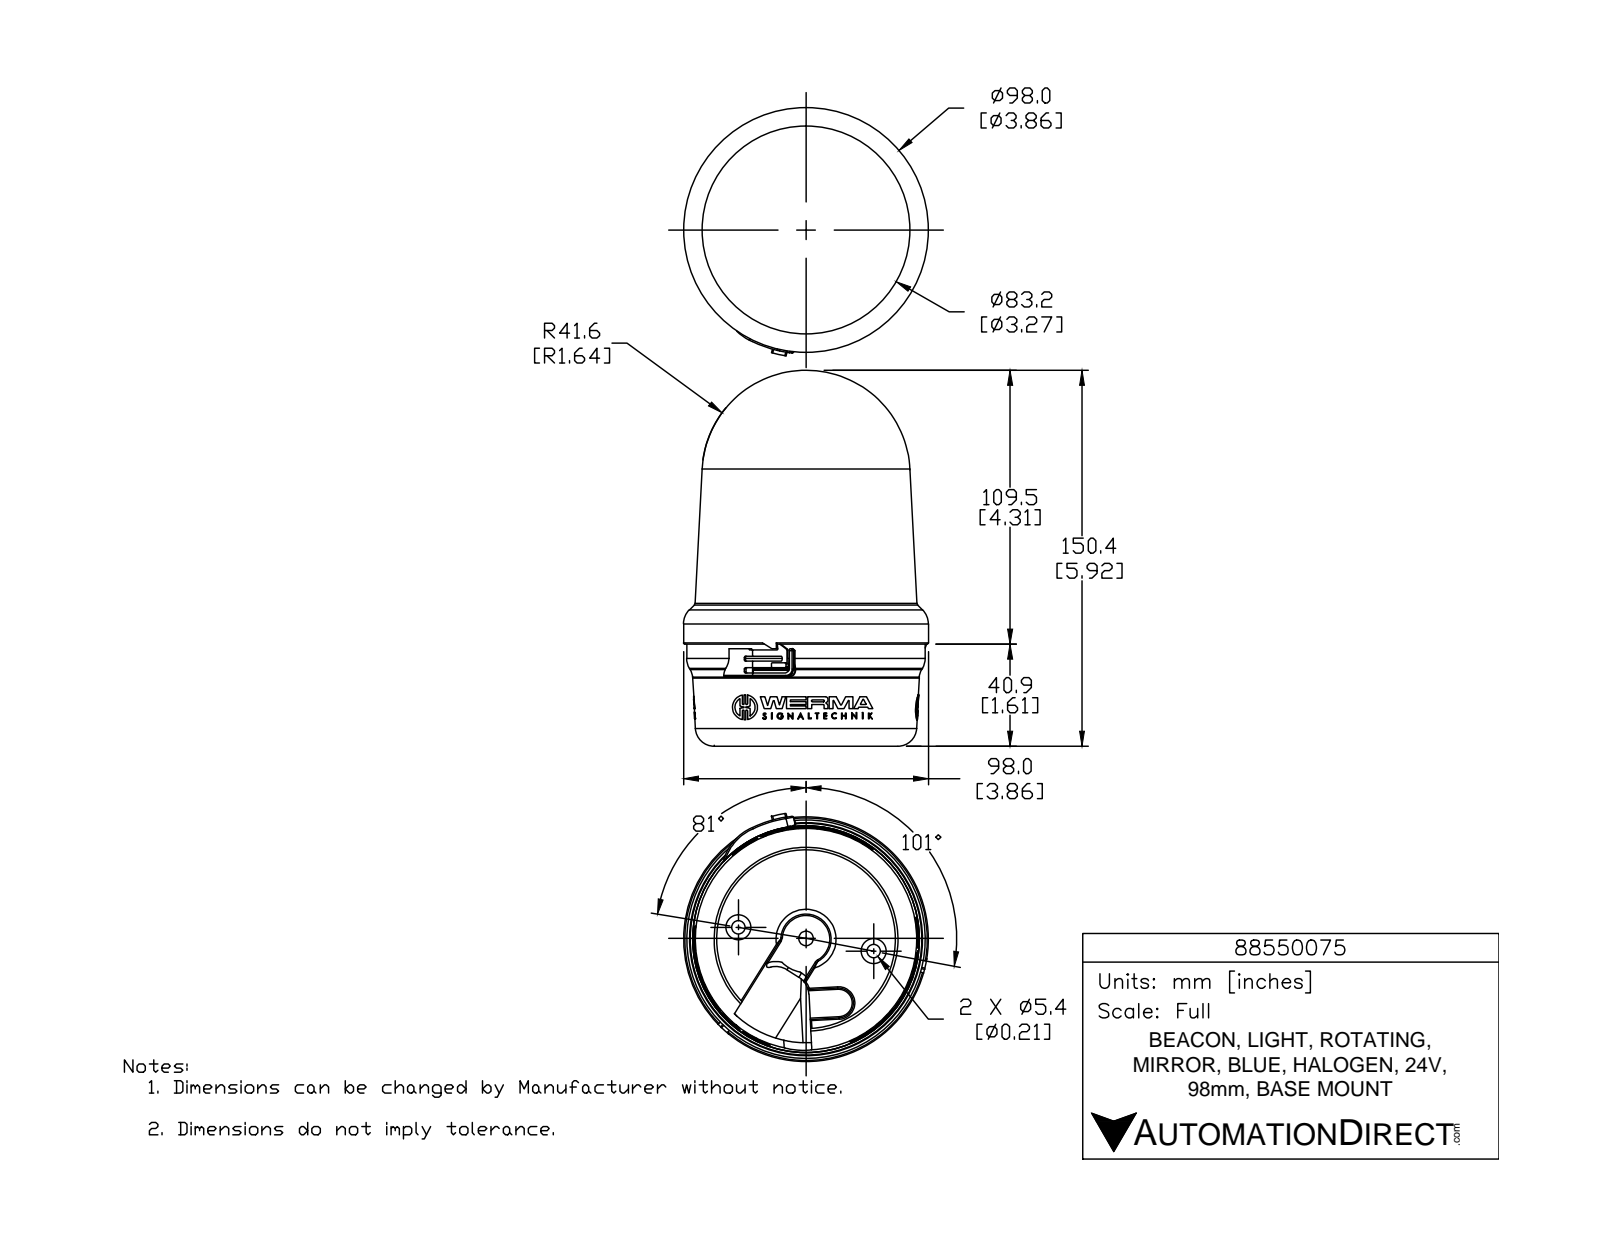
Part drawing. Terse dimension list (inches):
name: 88550075
written by: SolidWorks 2015 (AUTOMOTIVE_DESIGN)
unit: in
bodies: 1 solid, 969 faces (586 planar, 238 cylindrical, 145 other)
size: 5.921 × 3.912 × 3.858
volume: 49.51 in³; area: 82.1 in²
holes: 3× ⌀0.068, 2× ⌀0.213, 2× ⌀0.409, 1× ⌀2.815
bosses: 3× ⌀0.395, 3× ⌀0.099, 2× ⌀0.394, 1× ⌀3.858, 1× ⌀3.756, 1× ⌀3.571
rounds: 21× R0.02, 9× R0.006, 6× R0.006, 6× R0.014, 6× R0.014, 6× R0.014, 6× R0.229, 4× R0.079
face distances: 0.059, 0.033, 0.27, 0.02, 0.289, 0.734, 0.768, 0.315, 1.319, 1.26
hole spacings: 1.083, 2.165
